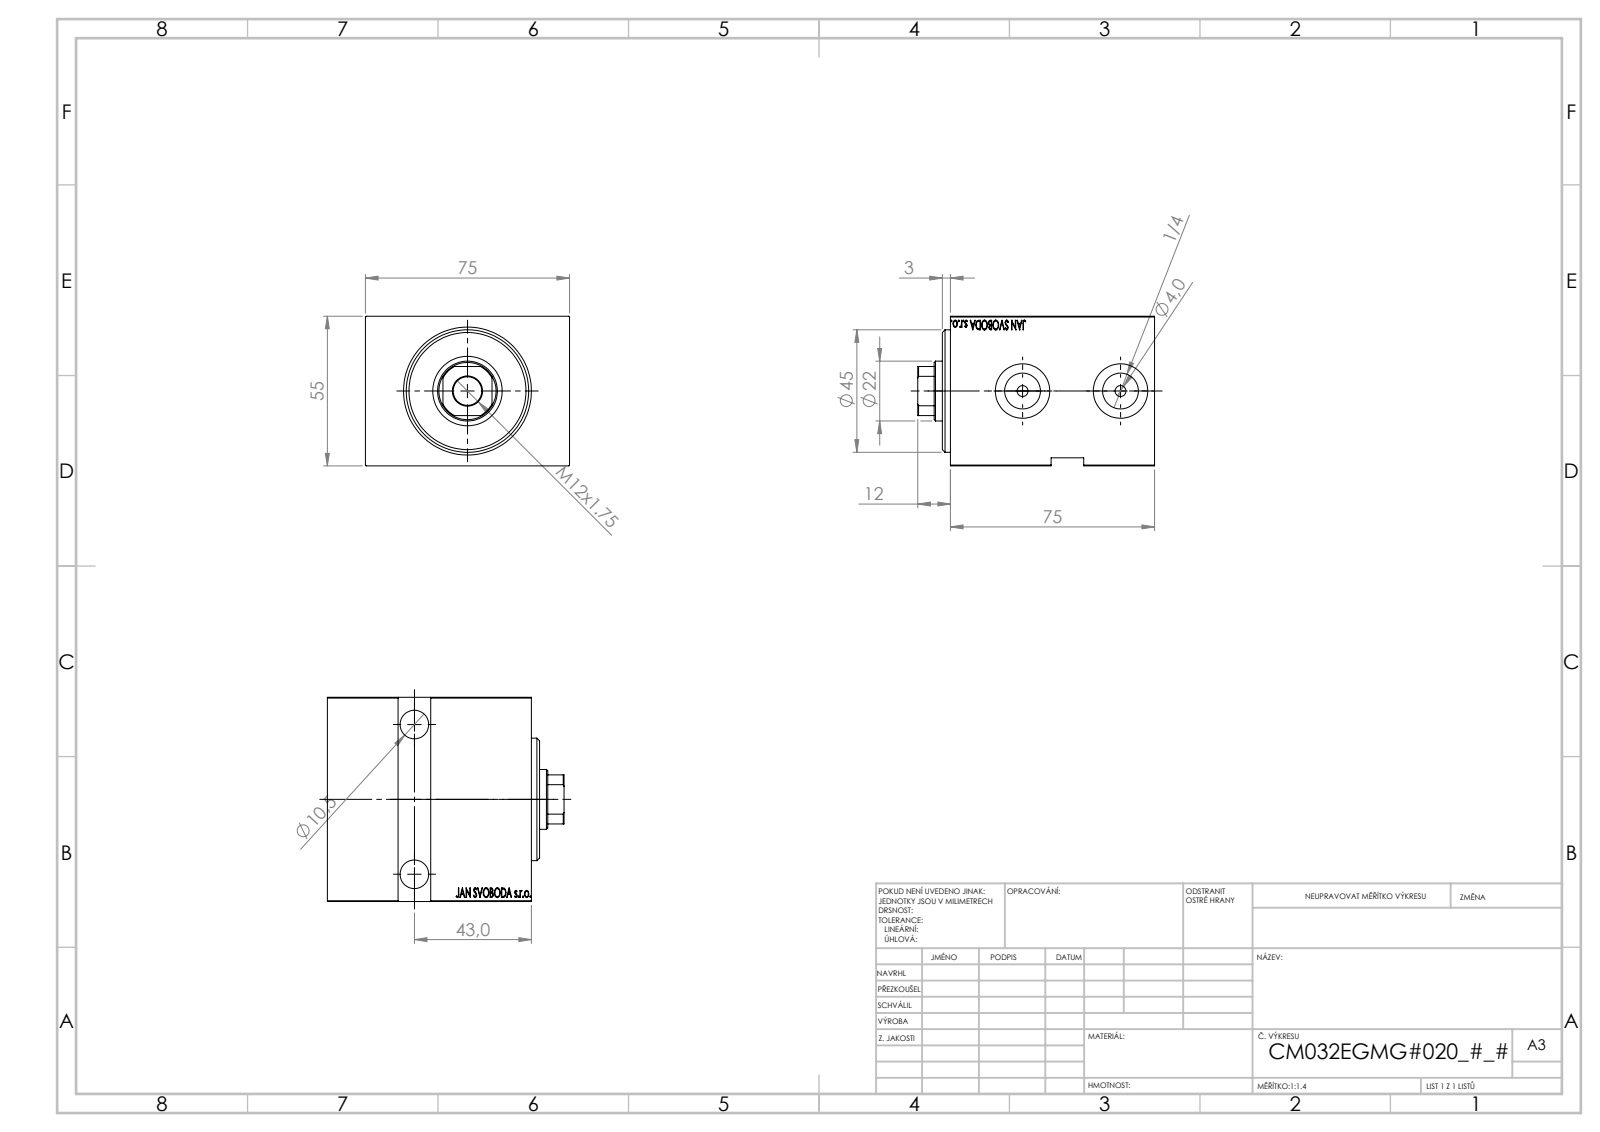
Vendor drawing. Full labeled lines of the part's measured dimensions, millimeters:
Part name (STEP PRODUCT): V450CM_VC_B; V450CM_E_VCP; V450CM_E_Body
STEP written by: SolidWorks 2019 (CONFIG_CONTROL_DESIGN)
Units: millimetres
Bodies: 3 solids, 848 faces (410 planar, 44 cylindrical, 394 other)
Overall size (bounding box): 87 × 75 × 55
Volume: 282 909 mm³ · Surface area: 54 129 mm²
Round holes (diameter × count): ⌀10.5 ×3, ⌀4 ×2, ⌀13.16 ×2, ⌀16.5 ×2, ⌀20 ×2, ⌀22 ×1, ⌀25.5 ×1, ⌀32 ×1, ⌀34 ×1, ⌀45 ×1
Partial cylindrical surfaces — rounded edges, fillets, slot ends (radius × count): R10.5 ×1
Main face-to-face distances: 75, 55, 3, 65, 10, 5, 70, 60, 8, 52
Hole centre spacings: 36, 55
